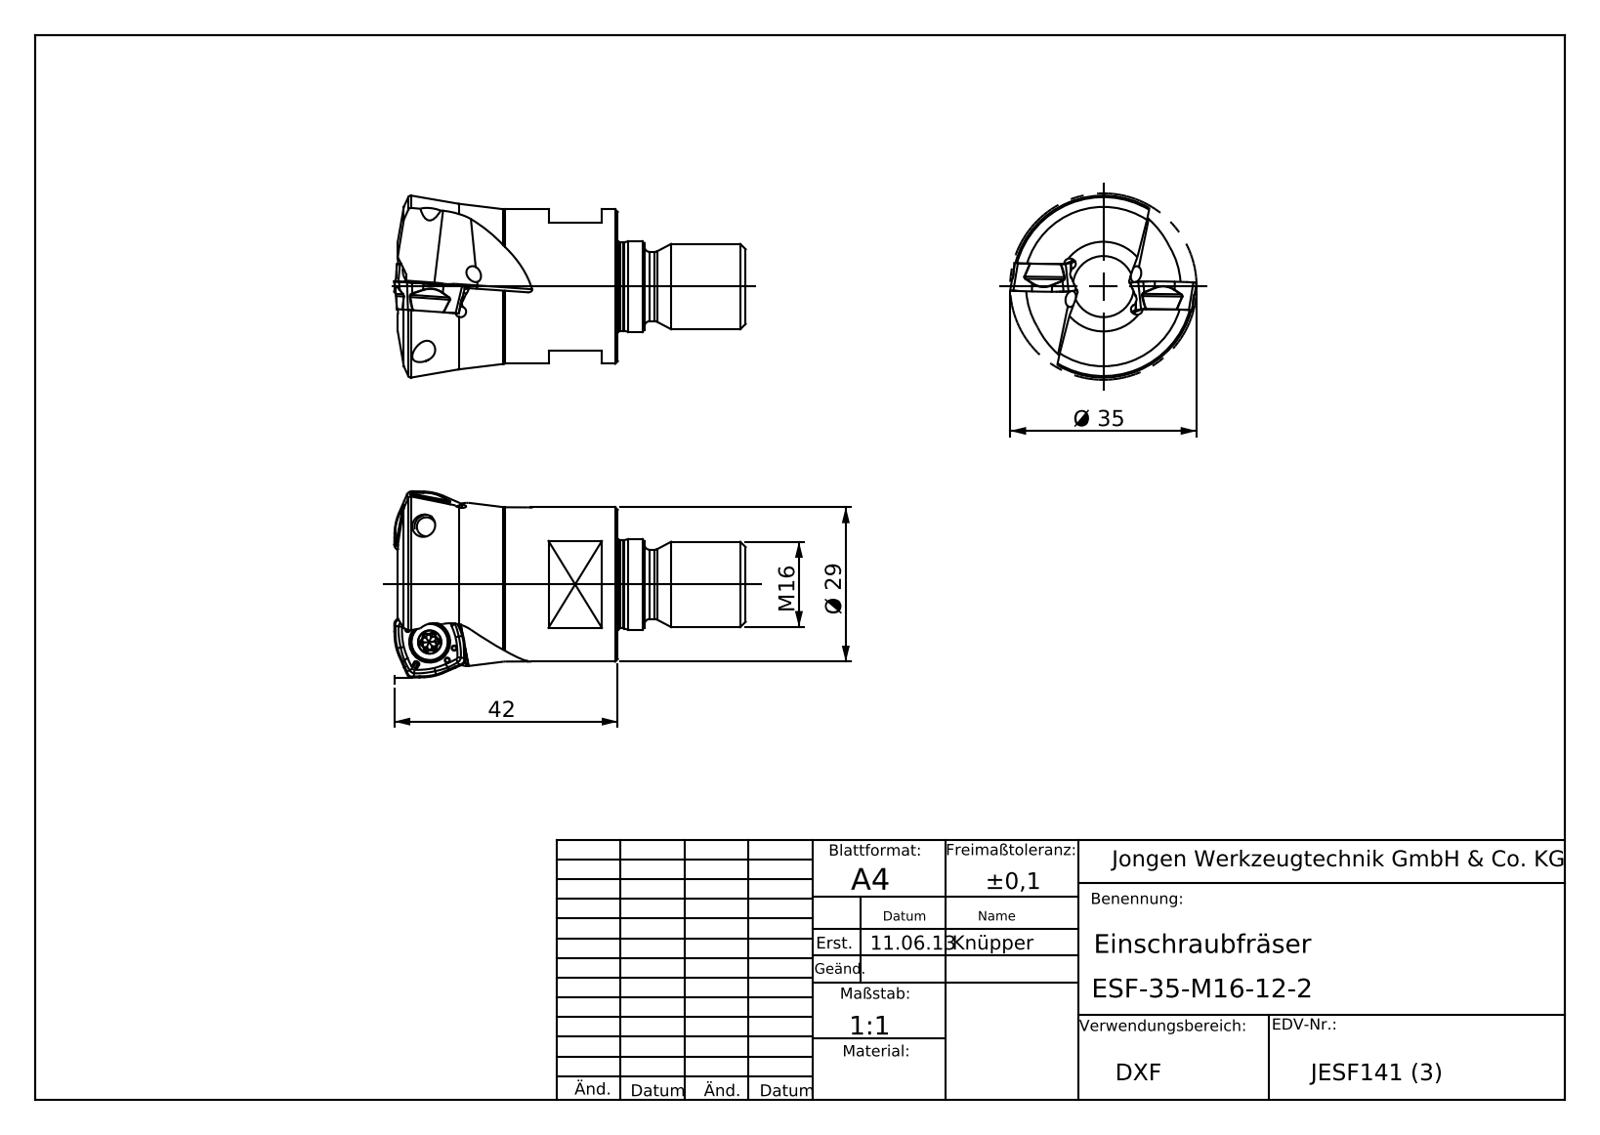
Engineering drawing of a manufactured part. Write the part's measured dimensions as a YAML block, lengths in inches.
part_name: "ESF-35-M16-12-2"
step_written_by: "SolidWorks 2013 (AUTOMOTIVE_DESIGN)"
units: inches
bodies: {solids: 1, faces: 118, planar: 47, cylindrical: 29, other: 42}
overall_size: [2.596, 1.377, 1.377]
volume: 1.978
surface_area: 12.38
round_holes:
  - {diameter: 0.118, count: 2}
  - {diameter: 0.157, count: 1}
round_bosses_or_shafts:
  - {diameter: 1.142, count: 1}
  - {diameter: 0.669, count: 1}
  - {diameter: 0.652, count: 1}
  - {diameter: 0.63, count: 1}
  - {diameter: 0.512, count: 1}
partial_cylinders:
  - {radius: 0.02, count: 4}
  - {radius: 0.051, count: 4}
  - {radius: 0.039, count: 2}
  - {radius: 0.079, count: 2}
face_to_face_distances: [0.945, 2.51, 1.565, 1.457, 0.512, 1.053, 1.063, 0.118, 0.394, 1.447]
